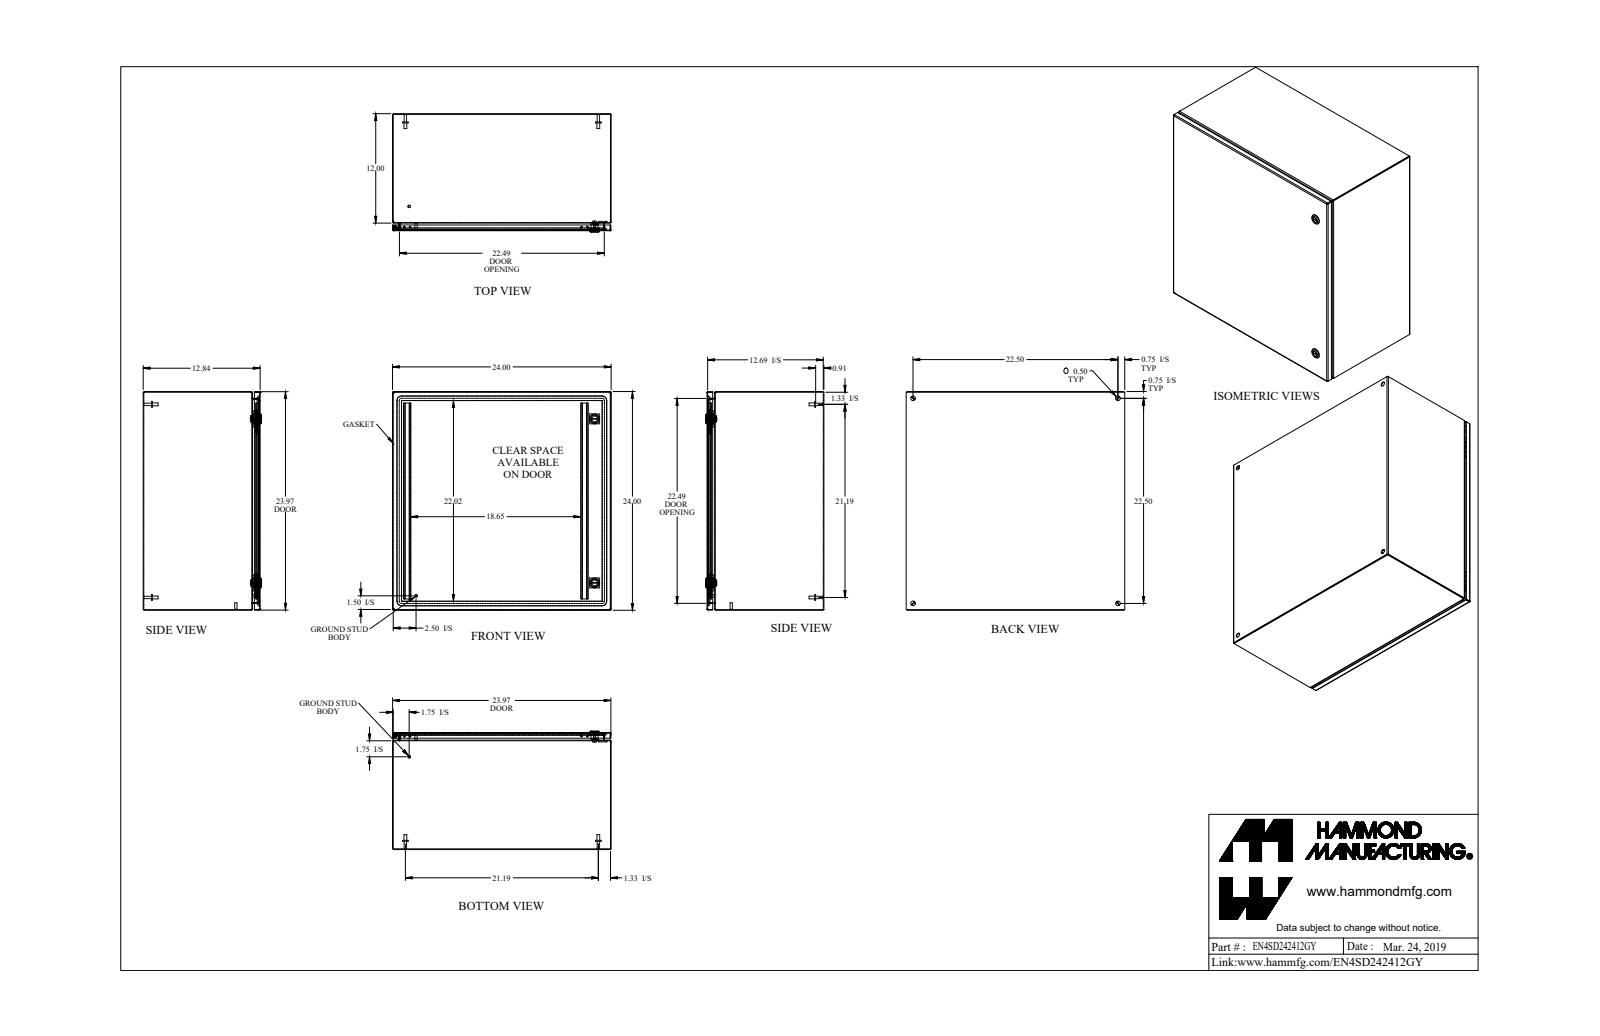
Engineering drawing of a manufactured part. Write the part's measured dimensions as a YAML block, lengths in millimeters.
part_name: "EN4SD242412GY"
step_written_by: "SolidWorks 2019 (AUTOMOTIVE_DESIGN)"
units: millimeters
bodies: {solids: 29, faces: 736, planar: 363, cylindrical: 245, other: 128}
overall_size: [609.6, 609.6, 330.1]
volume: 3135000
surface_area: 3458000
round_holes:
  - {diameter: 12.7, count: 4}
  - {diameter: 5.9, count: 2}
  - {diameter: 15.9, count: 2}
  - {diameter: 19.9, count: 2}
  - {diameter: 4.4, count: 1}
  - {diameter: 6.1, count: 1}
  - {diameter: 6.1, count: 1}
round_bosses_or_shafts:
  - {diameter: 15.9, count: 4}
  - {diameter: 8, count: 4}
  - {diameter: 6.9, count: 4}
  - {diameter: 27.9, count: 2}
  - {diameter: 13.3, count: 2}
  - {diameter: 7.1, count: 2}
  - {diameter: 6.4, count: 2}
  - {diameter: 11.6, count: 1}
partial_cylinders:
  - {radius: 0.9, count: 14}
  - {radius: 2.7, count: 14}
  - {radius: 1.1, count: 12}
  - {radius: 2.1, count: 12}
  - {radius: 7.9, count: 12}
  - {radius: 2.5, count: 8}
  - {radius: 0.2, count: 4}
  - {radius: 1.6, count: 4}
face_to_face_distances: [1.8, 324.2, 607.8, 322.4, 605.9, 326.1, 609.6, 21.3, 303, 19.1]
hole_center_spacings: [571.5, 808.2, 63.3, 63.3, 457.2, 515, 515.1, 547.2]
